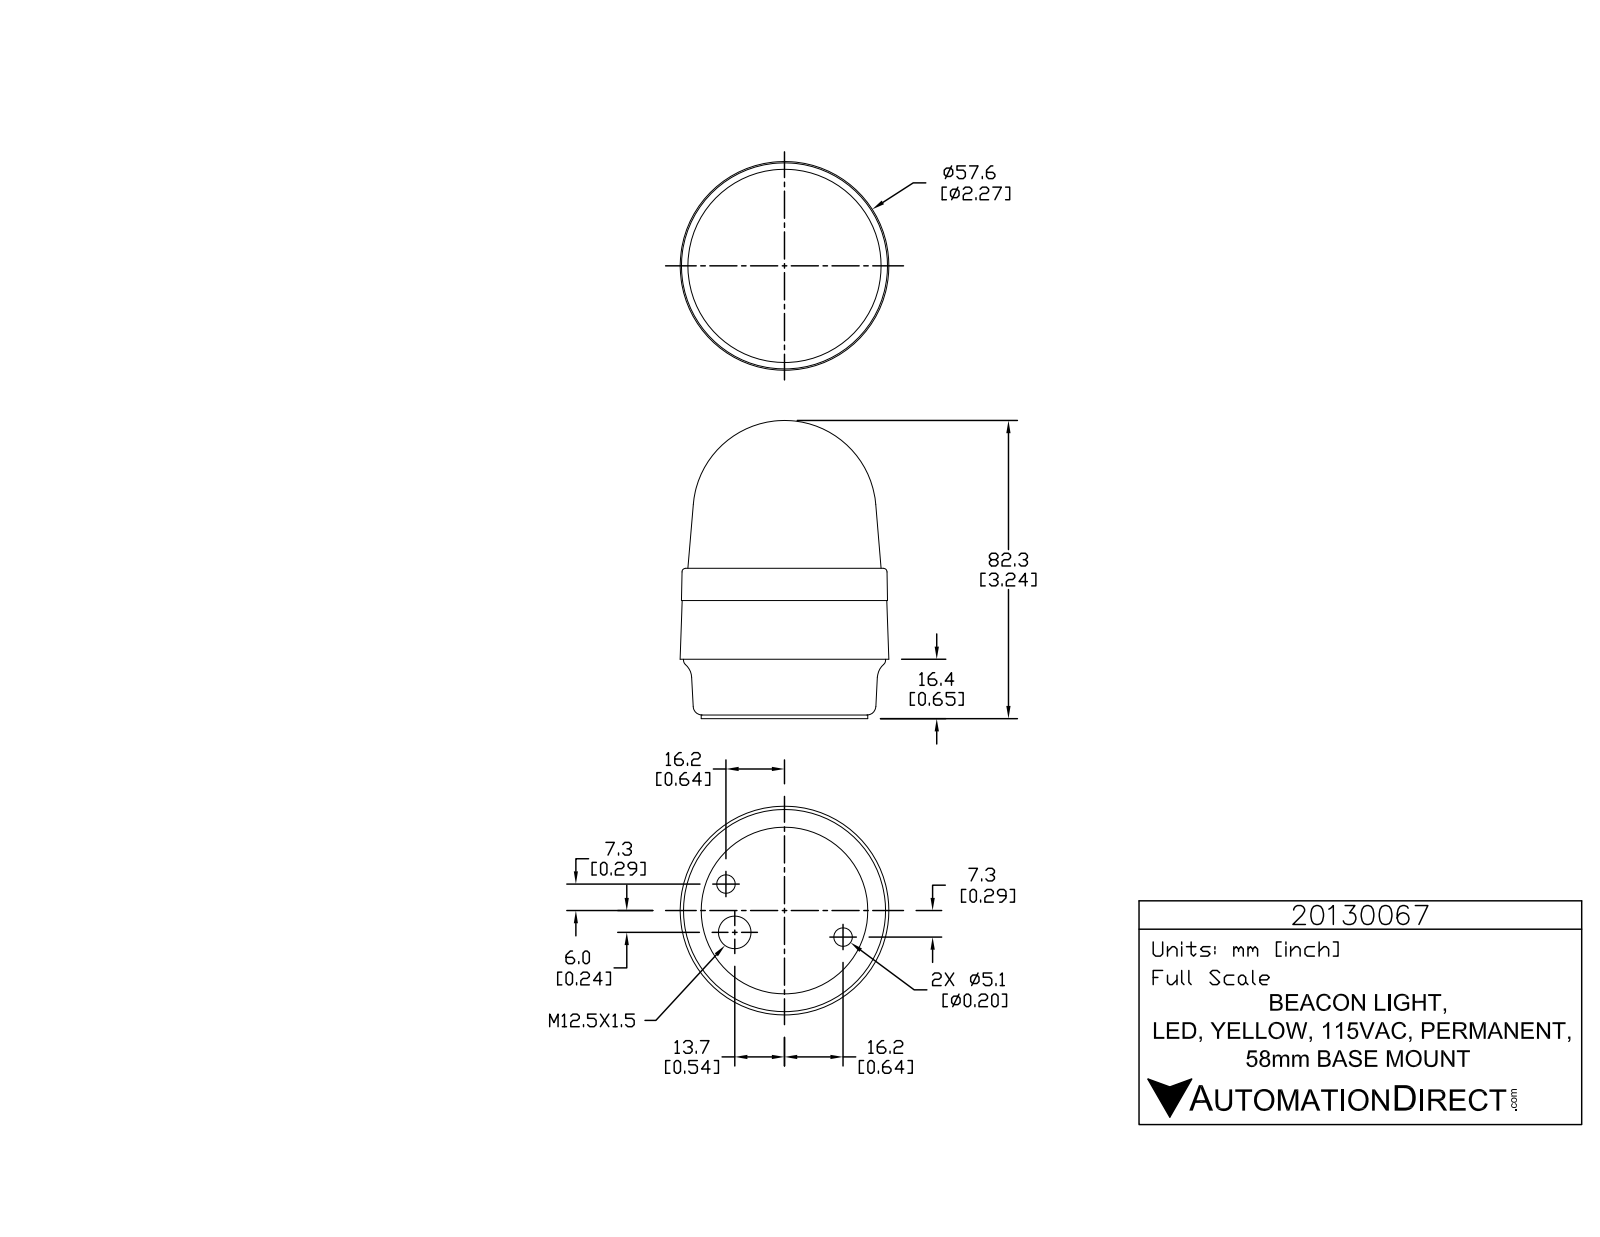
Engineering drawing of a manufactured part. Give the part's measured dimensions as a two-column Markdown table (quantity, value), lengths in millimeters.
| quantity | value |
| --- | --- |
| part name | 20130067 |
| STEP written by | SolidWorks 2015 (AUTOMOTIVE_DESIGN) |
| units | millimeters |
| bodies | 1 solid, 763 faces (527 planar, 145 cylindrical, 91 other) |
| overall size | 82.3 × 57.63 × 57.63 |
| volume | 164 395 mm³ |
| surface area | 16 261 mm² |
| round holes (diameter × count) | 0.99 × 3, 5.11 × 2, 9 × 1 |
| round bosses / shafts (diameter × count) | 5.74 × 3, 1.43 × 3, 55.8 × 1, 46 × 1 |
| partial cylindrical surfaces (radius × count) | 0.2 × 6, 0.21 × 6, 0.21 × 6, 3.32 × 6, 0.1 × 3, 0.12 × 3, 0.19 × 3, 0.2 × 3 |
| main face-to-face distances | 16.4, 1, 15.4, 41.5, 40.5, 25.1, 32.6, 31.6, 16.2, 8.9 |
| hole center spacings | 13.56, 29.94, 35.5 |
